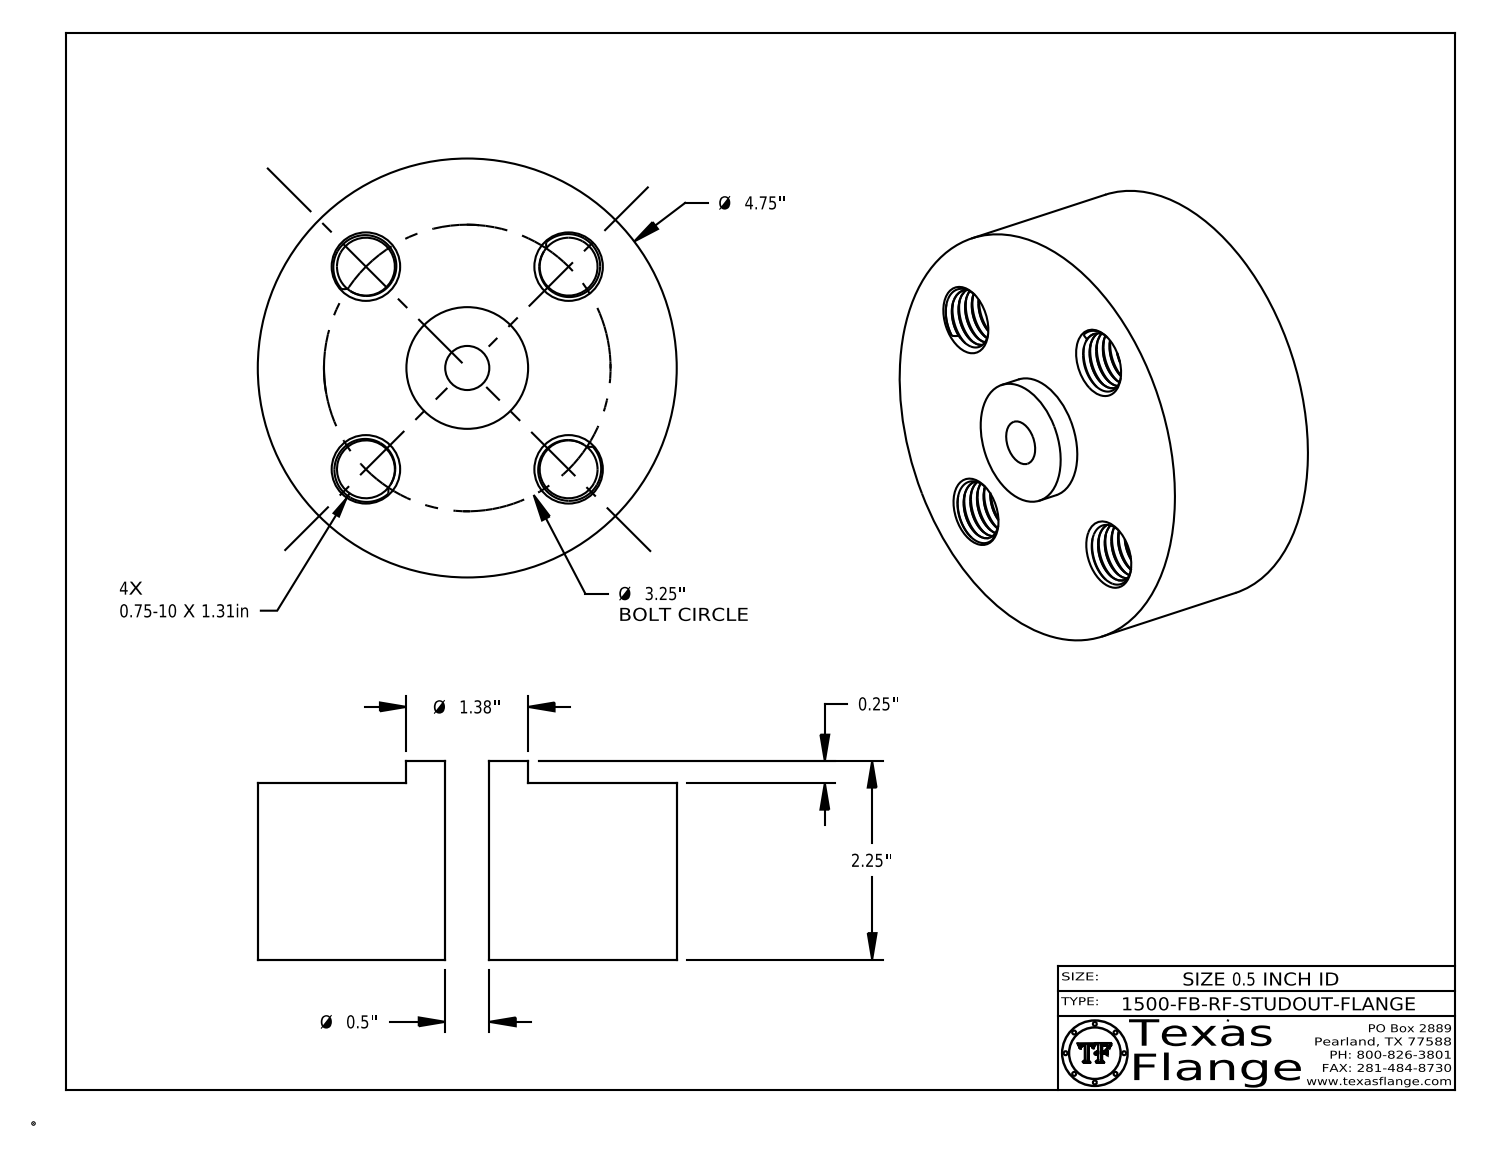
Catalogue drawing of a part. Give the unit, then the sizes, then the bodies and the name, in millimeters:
Units: millimetres
Overall size (bounding box): 120.7 × 120.7 × 57.2
Round holes (diameter × count): ⌀16.7 ×4, ⌀12.7 ×1, ⌀25.4 ×1
Round bosses / shafts (diameter × count): ⌀1.5 ×8, ⌀120.7 ×1, ⌀35.1 ×1, ⌀20 ×1
Main face-to-face distances: 50.8, 6.4, 57.2, 0.4, 56.8, 50.4, 7.6, 7.4, 1.4, 6.3
Hole centre spacings: 41.3, 58.4, 31.6, 76.3, 82.6
Volume: 546 300 mm³ · Surface area: 53 860 mm²
Bodies: 1 solid, 634 faces (368 planar, 106 cylindrical, 160 other)
Part name (STEP PRODUCT): 0.5-1500-FB-RF-STUDOUT-FLANGE
STEP written by: CATIA V5 STEP AP214 (AUTOMOTIVE_DESIGN)
